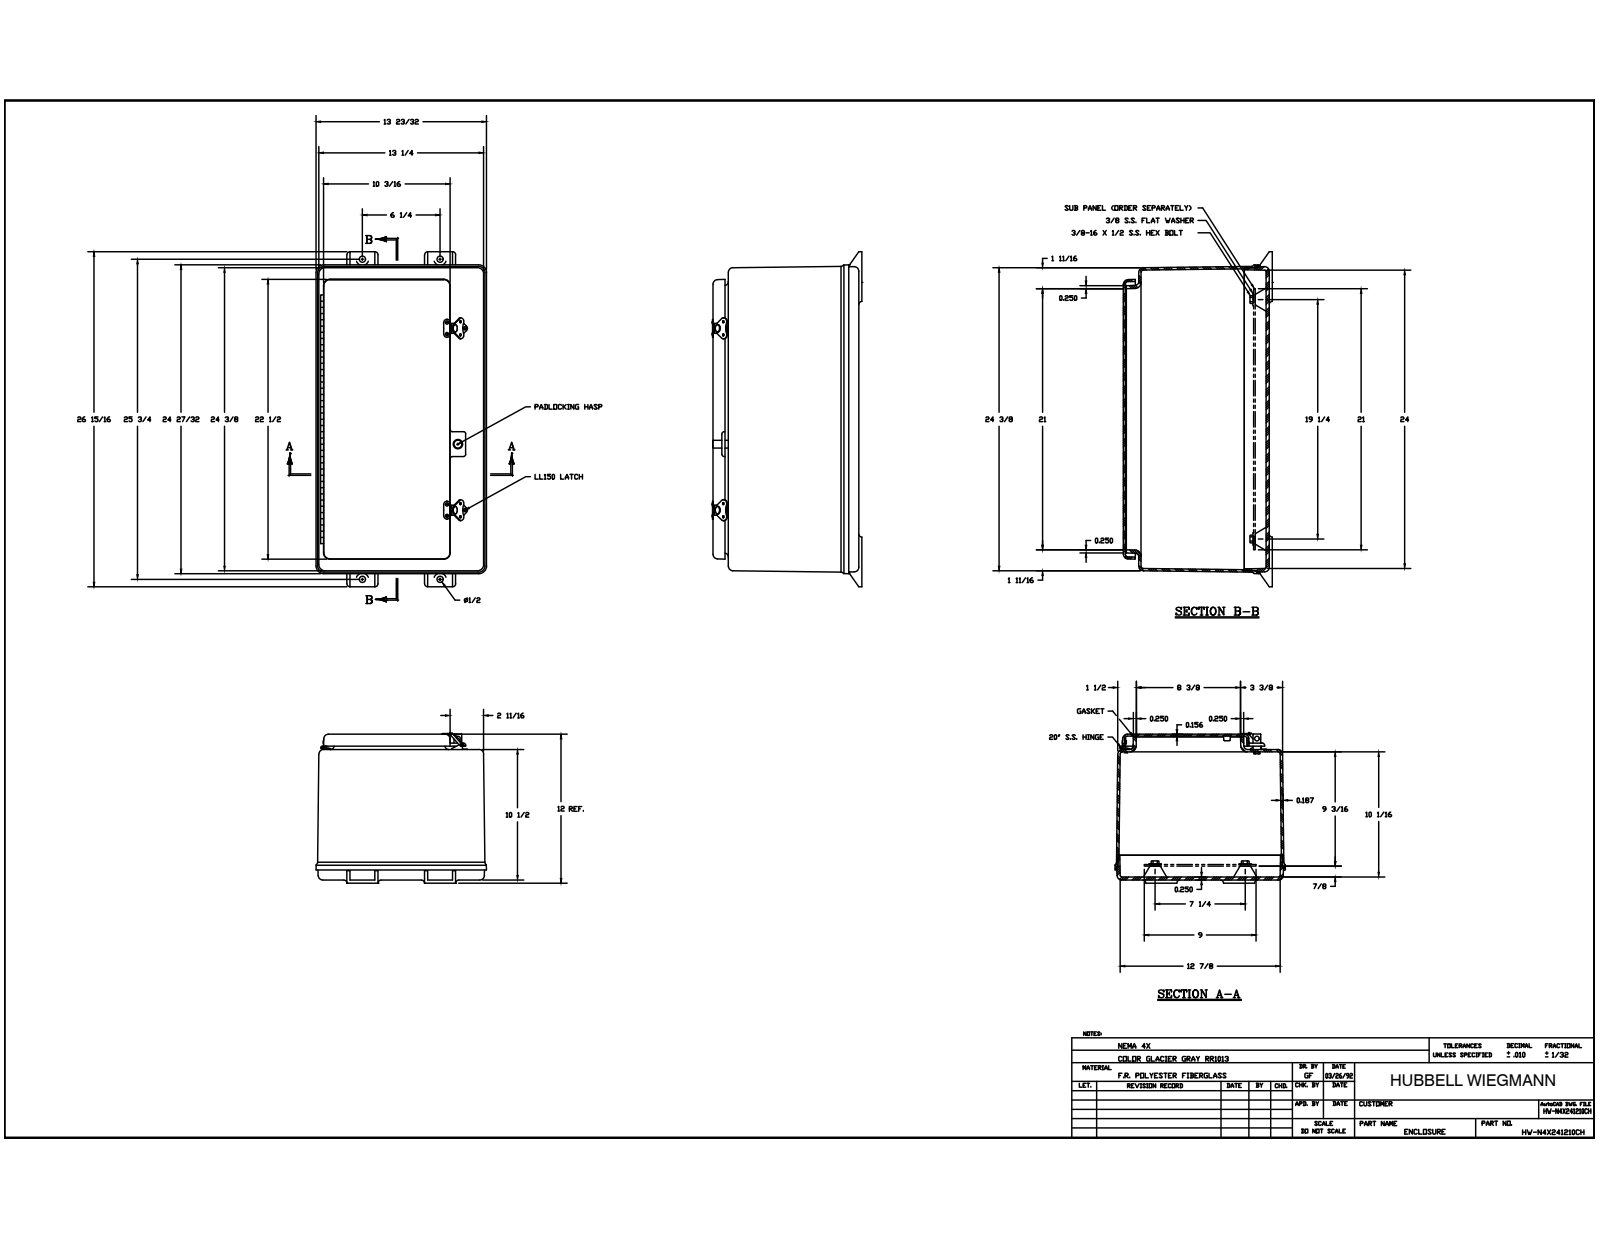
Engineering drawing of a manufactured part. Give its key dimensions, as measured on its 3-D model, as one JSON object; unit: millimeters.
{"part_name": "WPN241210SHWT; WPN2412B; WPN241210HWTPCVR; N241210G (+8 more)", "step_written_by": "Autodesk Inventor 2014 (AUTOMOTIVE_DESIGN)", "units": "millimeters", "bodies": {"solids": 38, "faces": 1151, "planar": 454, "cylindrical": 446, "other": 251}, "overall_size": [684.21, 348.46, 310.01], "volume_mm3": 5415000, "surface_area_mm2": 2276000, "round_holes": [[3.3, 21], [1.59, 8], [1.65, 8], [3.5, 4], [4.76, 4], [14.3, 4], [3.68, 2], [7.14, 2], [12.95, 2], [12.96, 2], [3.17, 1], [3.43, 1]], "round_bosses_or_shafts": [[7.54, 8], [3.56, 8], [12.7, 2], [7.14, 1], [6.35, 1], [5.11, 1], [5.08, 1], [3.17, 1]], "partial_cylinders_radius": [[0.25, 59], [6.35, 24], [4.76, 21], [12.7, 12], [7.94, 10], [9.53, 10], [0.76, 8], [3.17, 6]], "face_to_face_distances": [4.75, 6.35, 3.97, 298.46, 292.11, 294.49, 288.14, 266.69, 261.94, 255.59], "hole_center_spacings": [23.81, 37.65, 161.92, 320.68, 361.34, 371.47, 385.04, 371.48]}
